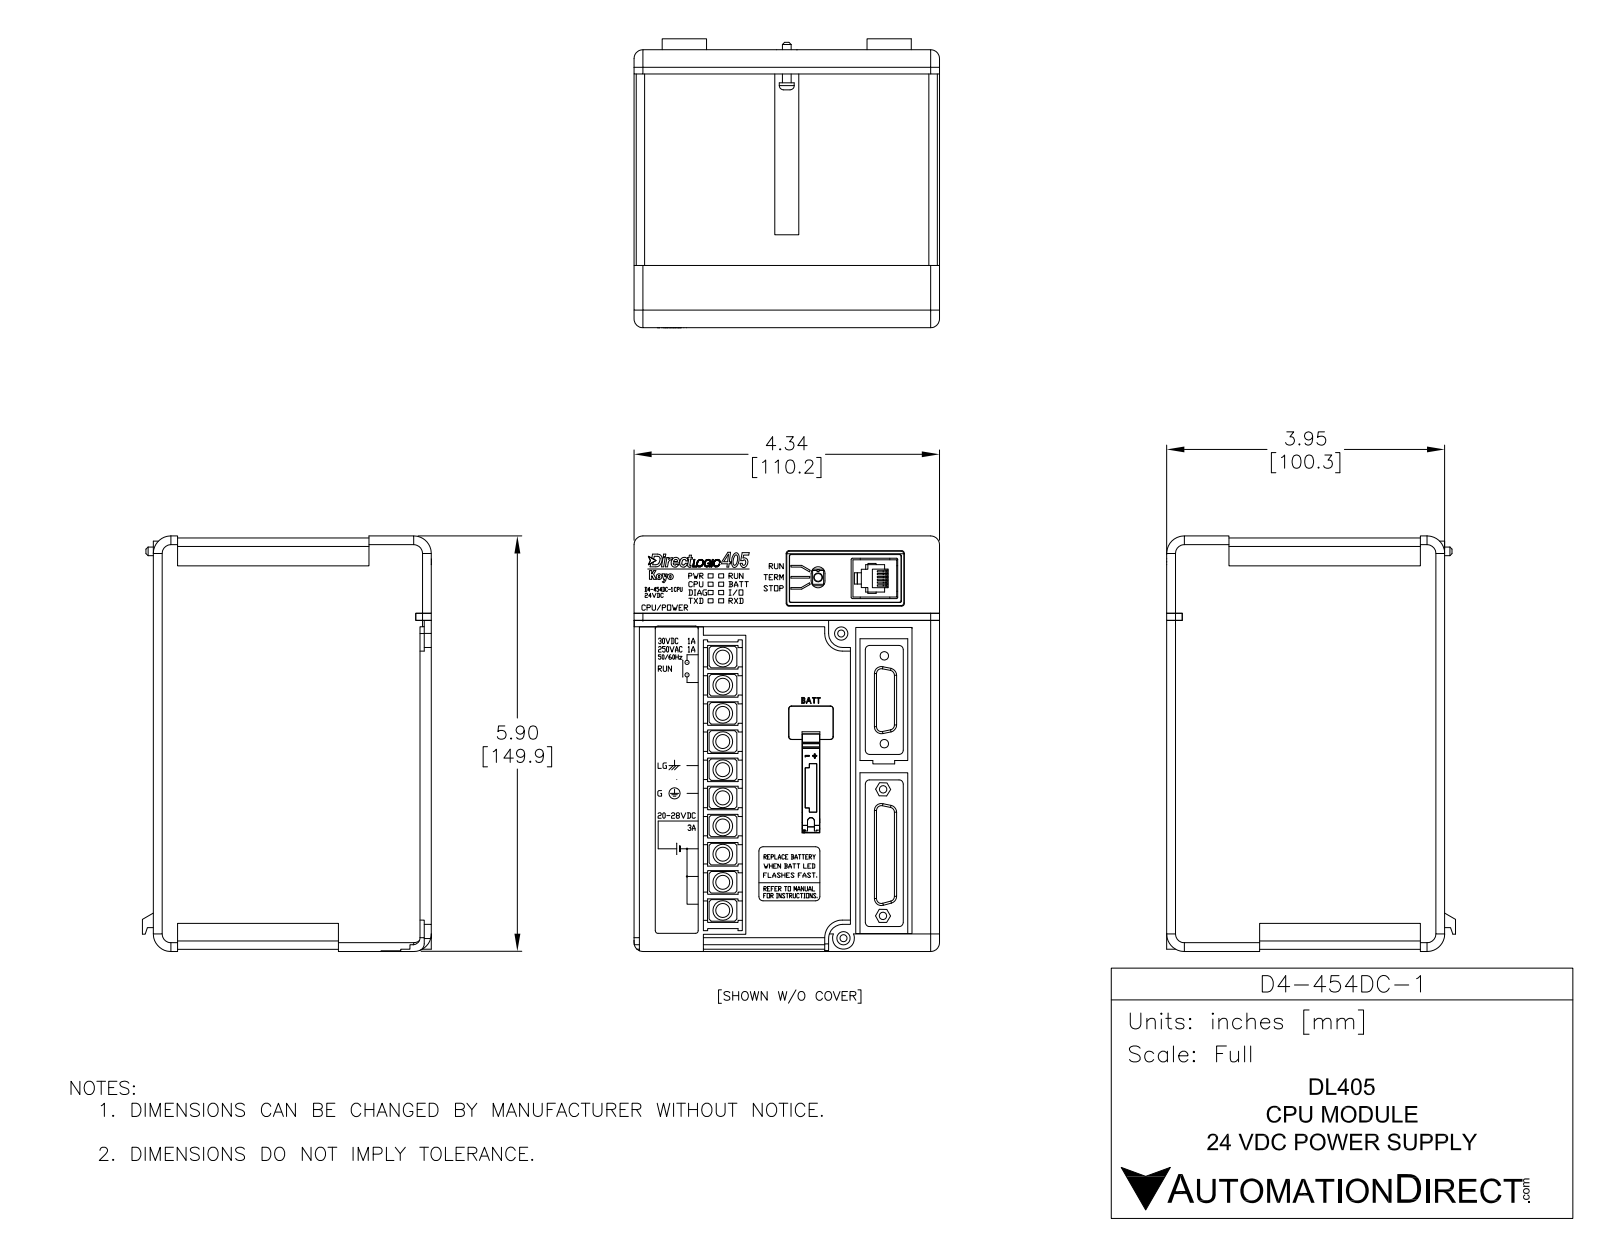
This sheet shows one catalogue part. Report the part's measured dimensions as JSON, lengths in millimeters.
{"part_name": "D4-454DC-1", "step_written_by": "SolidWorks 2016 (AUTOMOTIVE_DESIGN)", "units": "millimeters", "bodies": {"solids": 9, "faces": 4600, "planar": 4158, "cylindrical": 379, "other": 63}, "overall_size": [150, 110.2, 104.3], "volume_mm3": 1439000, "surface_area_mm2": 136400, "round_holes": [[1.4, 2], [2.5, 2], [3, 2], [2.6, 1], [2.7, 1], [3.2, 1], [3.9, 1], [4.8, 1], [4.8, 1]], "round_bosses_or_shafts": [[7.1, 10], [2.1, 2], [1.6, 2], [5.4, 1], [4.1, 1], [3.1, 1]], "partial_cylinders_radius": [[1.3, 19], [1, 12], [2.5, 10], [2.6, 10], [2.5, 9], [3.2, 9], [0.9, 8], [1.5, 8]], "face_to_face_distances": [110.2, 0.8, 139.2, 149.2, 150, 10.8, 7.1, 132.1, 142.9, 10], "hole_center_spacings": [3.5, 16.4, 16.5, 17.5, 20.7, 31.7, 36.1, 42.7]}
